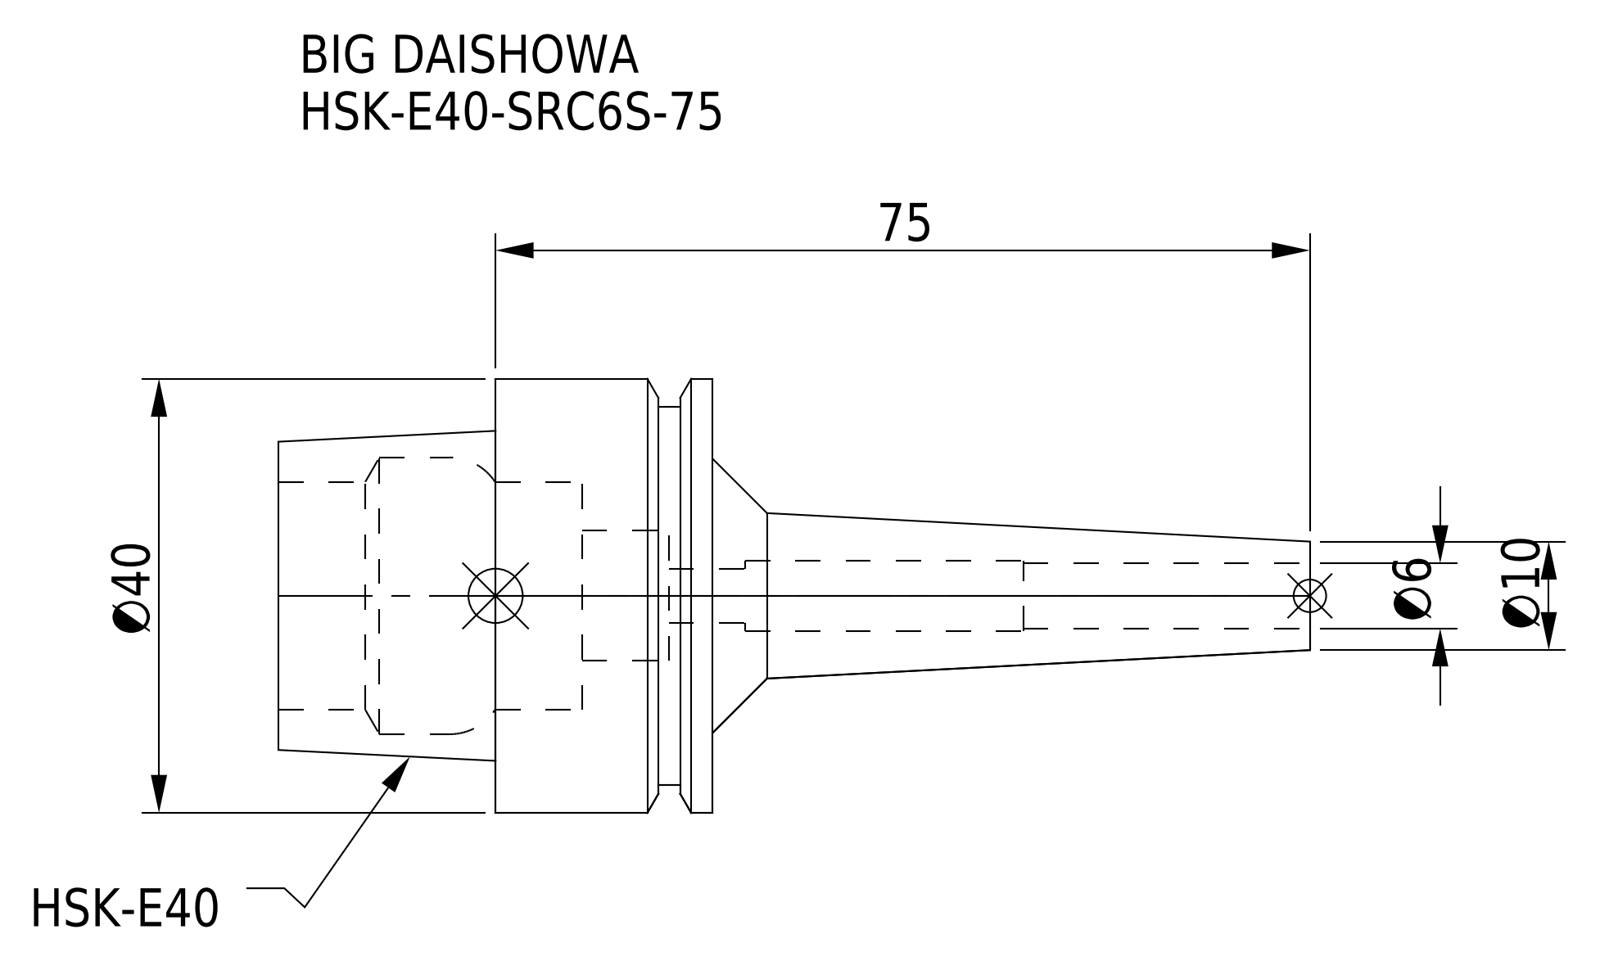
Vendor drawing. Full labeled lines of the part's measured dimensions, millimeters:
Part name (STEP PRODUCT): HSK-E40-SRC6S-75
STEP written by: CREO PARAMETRIC BY PTC INC, 2016380 (AUTOMOTIVE_DESIGN)
Units: millimetres
Bodies: 1 solid, 46 faces (10 planar, 22 cylindrical, 14 other)
Overall size (bounding box): 95 × 40 × 40
Volume: 31 909 mm³ · Surface area: 12 723 mm²
Round holes (diameter × count): ⌀5 ×1, ⌀6 ×1, ⌀6.5 ×1, ⌀12 ×1, ⌀21 ×1, ⌀25.5 ×1
Round bosses / shafts (diameter × count): ⌀40 ×1, ⌀34.8 ×1
Main face-to-face distances: 20, 40, 12.05, 7.95, 27.95, 8, 7.05, 3, 4.05, 15.95
